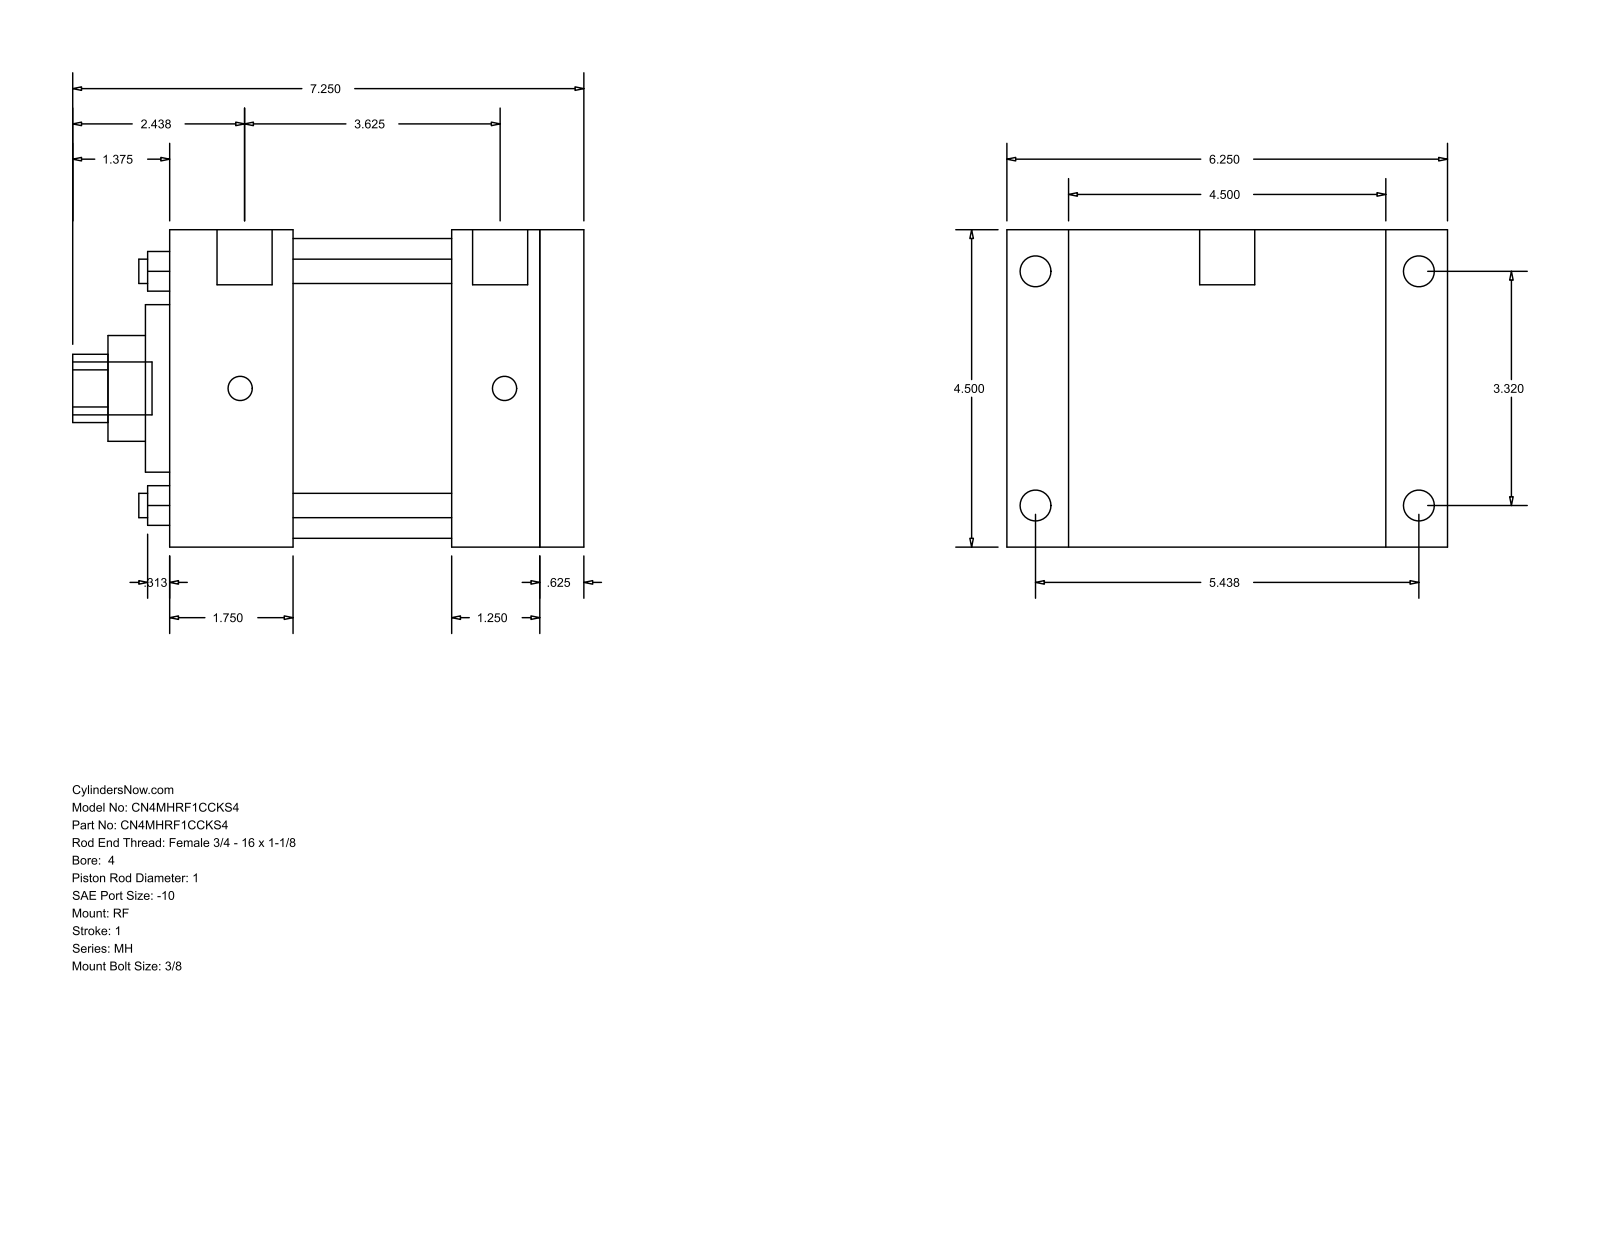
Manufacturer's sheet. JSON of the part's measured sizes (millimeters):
{"part_name": "MH_RF__0400_1", "step_written_by": "GSSL Pune (CONFIG_CONTROL_DESIGN)", "units": "millimeters", "bodies": {"solids": 0, "faces": 94, "planar": 65, "cylindrical": 29, "other": 0}, "overall_size": [184.15, 158.75, 114.3], "round_holes": [[8.76, 4], [25.4, 1], [38.1, 1], [60.33, 1], [107.95, 1]], "round_bosses_or_shafts": [[11.13, 4], [8.73, 4], [19.84, 2], [19.05, 1]], "partial_cylinders_radius": [[12.29, 1]], "face_to_face_distances": [114.3, 149.23, 15.87, 133.36, 136.53, 44.46, 88.9, 104.77, 101.61, 57.15], "hole_center_spacings": [59.62, 84.32, 119.25]}
